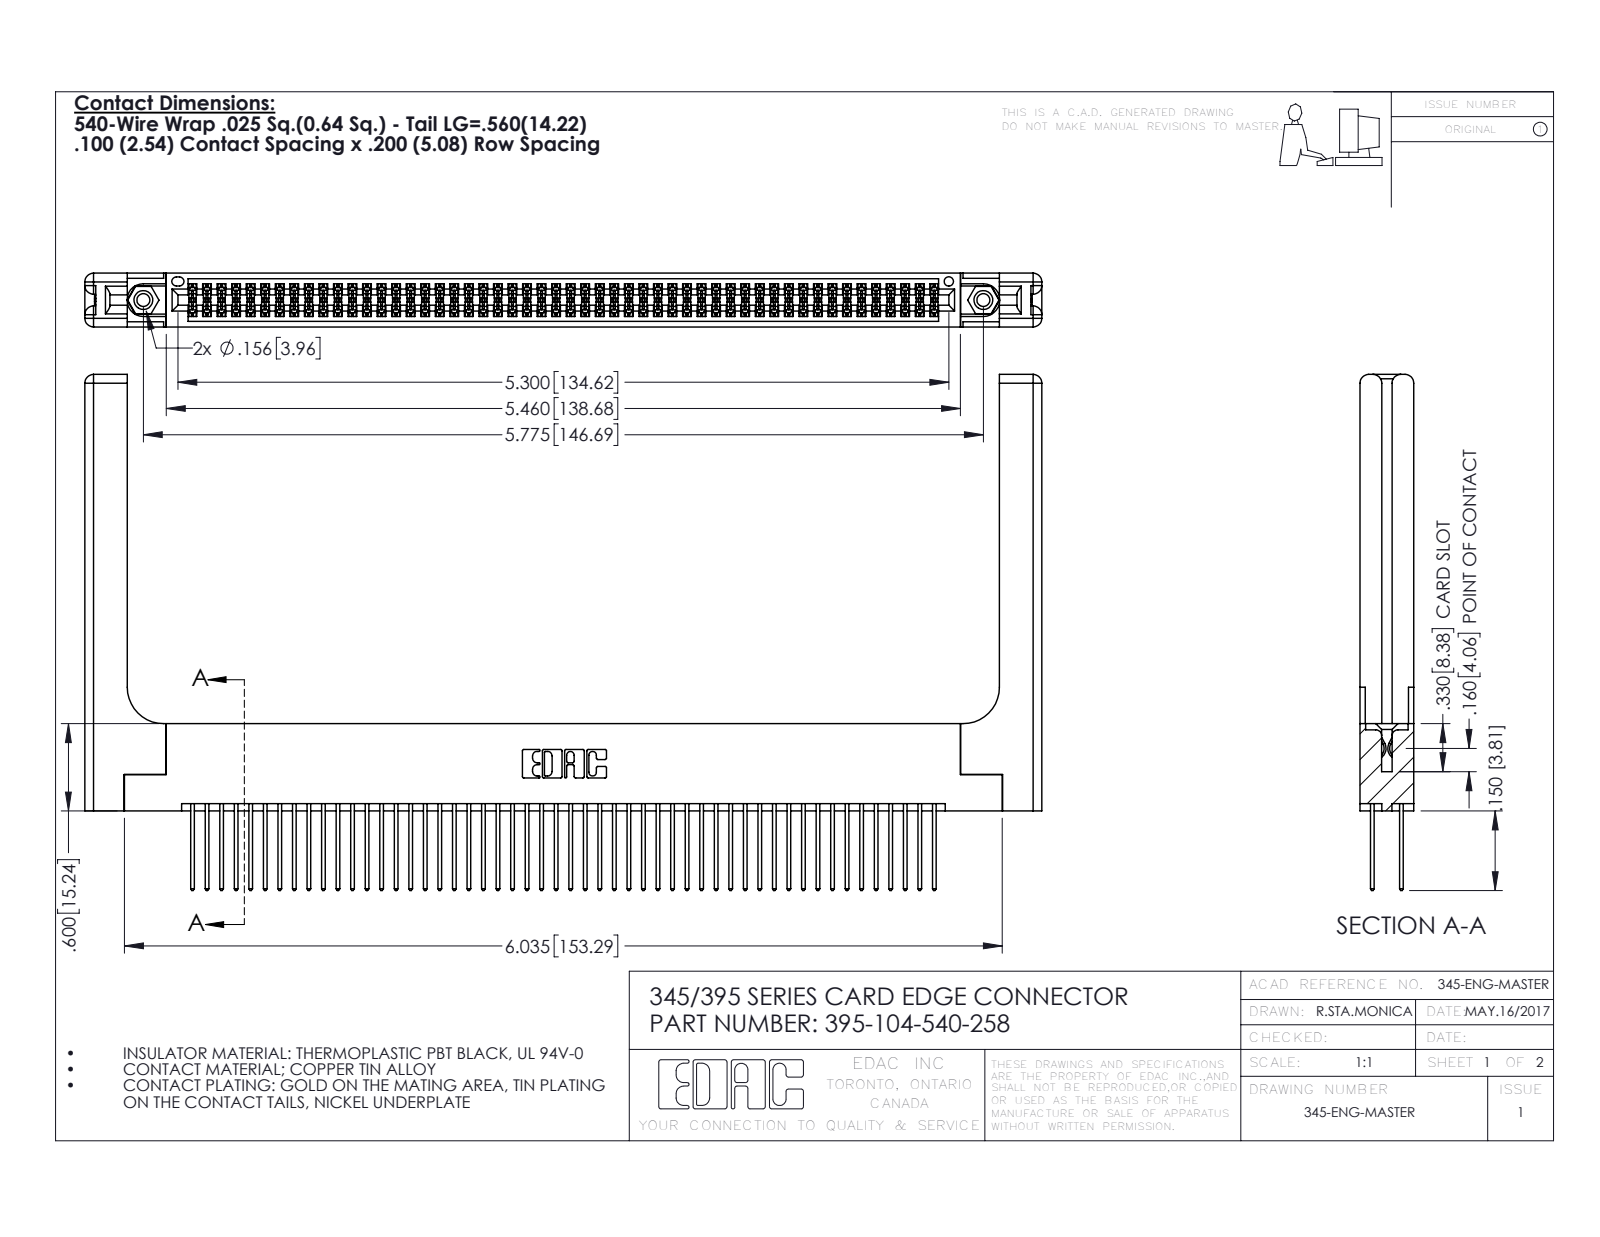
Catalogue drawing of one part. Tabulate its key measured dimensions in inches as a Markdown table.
| quantity | value |
| --- | --- |
| part name | 345 Part_Flush Mounting Lugs - 0.156 Dia-TH; 345-292-001_345-293-140; 345-220-058_345-220-058; 395-104-540-258 (+1 more) |
| STEP written by | SolidWorks 2016 (CONFIG_CONTROL_DESIGN) |
| units | inches |
| bodies | 109 solids, 5582 faces (3660 planar, 1862 cylindrical, 60 other) |
| overall size | 6.579 × 3.547 × 0.37 |
| volume | 1.538 in³ |
| surface area | 49.28 in² |
| round holes (diameter × count) | 0.089 × 2, 0.125 × 2, 0.156 × 2, 0.064 × 1 |
| round bosses / shafts (diameter × count) | 0.155 × 2 |
| partial cylindrical surfaces (radius × count) | 0.006 × 156, 0.01 × 104, 0.01 × 22, 0.06 × 16, 0.007 × 6, 0.031 × 6, 0.026 × 3, 0.014 × 2 |
| main face-to-face distances | 0.072, 0.298, 0.37, 0.2, 0.098, 0.272, 0.025, 0.225, 0.175, 0.148 |
| hole center spacings | 0.27, 5.539, 5.775 |
